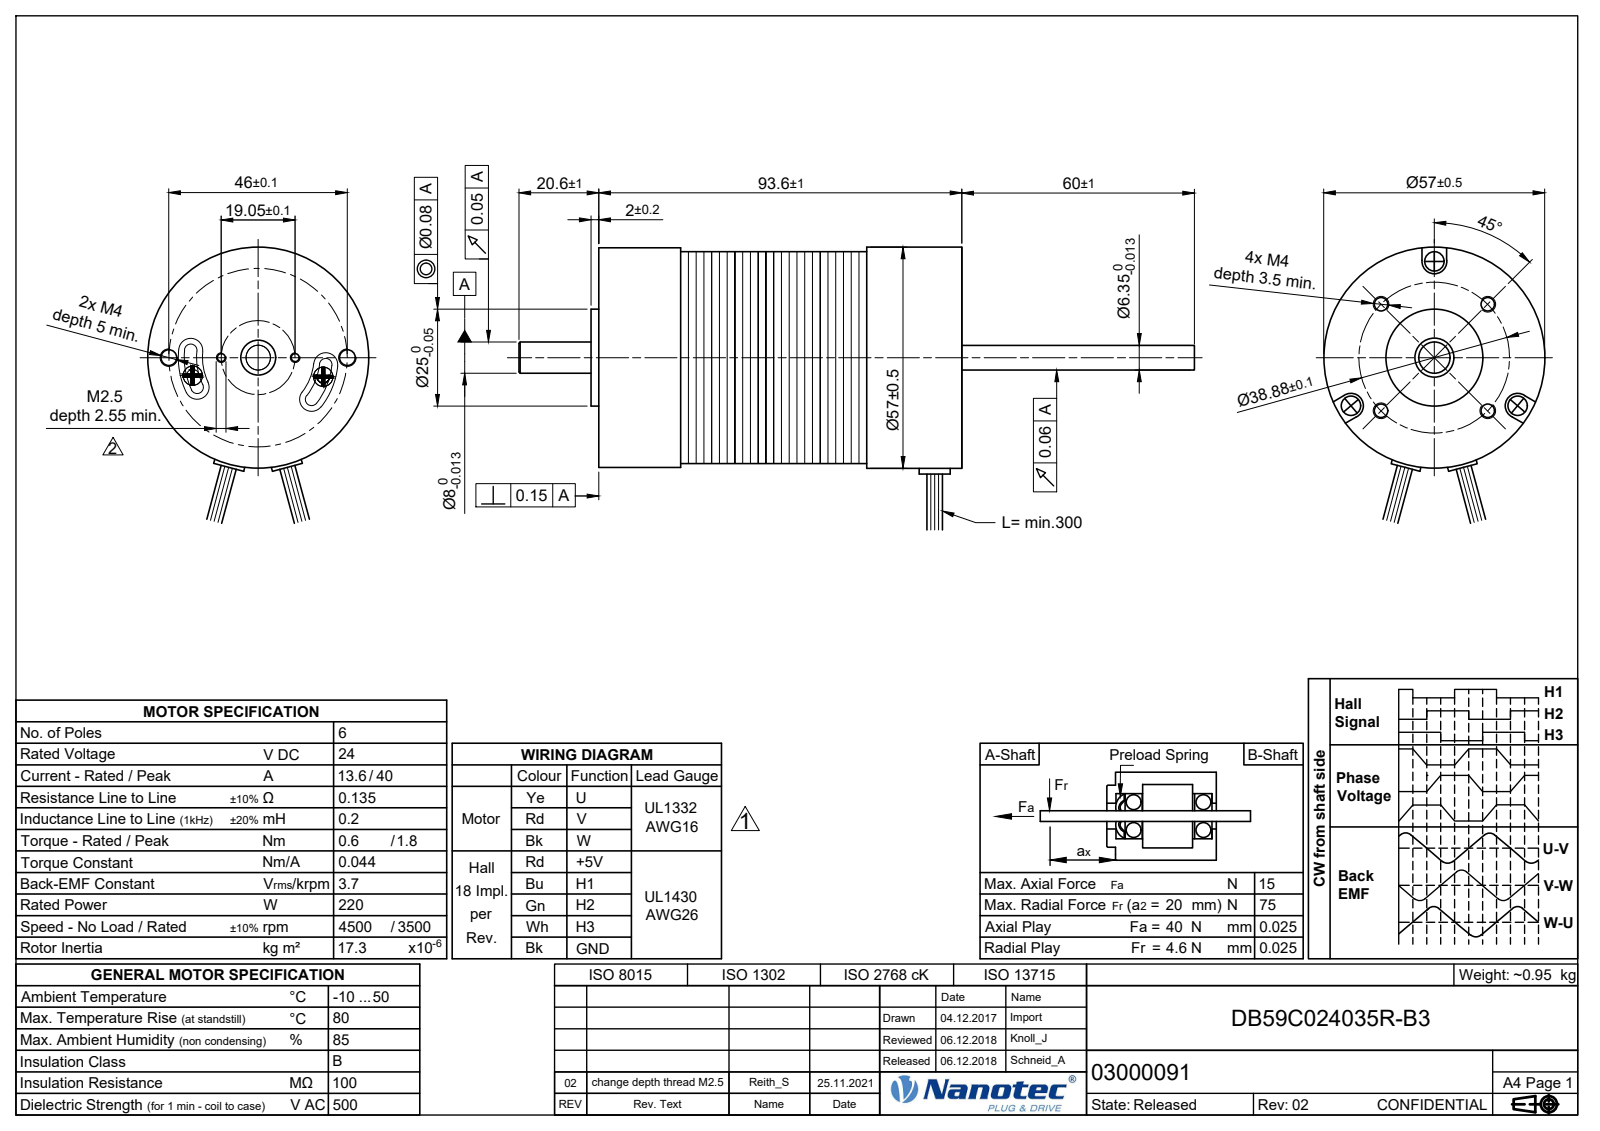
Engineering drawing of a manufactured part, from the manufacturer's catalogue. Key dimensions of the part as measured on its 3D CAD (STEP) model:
Part name (STEP PRODUCT): DB59C024035R-B3_Shrinkwrap_1
STEP written by: Autodesk Inventor 2019 (AUTOMOTIVE_DESIGN)
Units: millimetres
Bodies: 9 solids, 176 faces (83 planar, 34 cylindrical, 59 other)
Overall size (bounding box): 174.2 × 87.19 × 57
Volume: 233 318 mm³ · Surface area: 40 724 mm²
Round holes (diameter × count): ⌀3.24 ×6, ⌀3.4 ×3, ⌀2.01 ×2, ⌀8 ×1, ⌀8.5 ×1, ⌀13 ×1
Round bosses / shafts (diameter × count): ⌀3 ×3, ⌀2.75 ×3, ⌀11 ×2, ⌀5.5 ×2, ⌀57 ×1, ⌀55 ×1, ⌀25 ×1, ⌀6.35 ×1
Partial cylindrical surfaces — rounded edges, fillets, slot ends (radius × count): R3.25 ×3
Main face-to-face distances: 56, 23.1, 79.1, 93.6, 70.5, 14.5, 2, 95.6, 72.5, 16.5
Hole centre spacings: 19.44, 27.49, 24.8, 9.52, 13.48, 14.11, 14.66, 16
